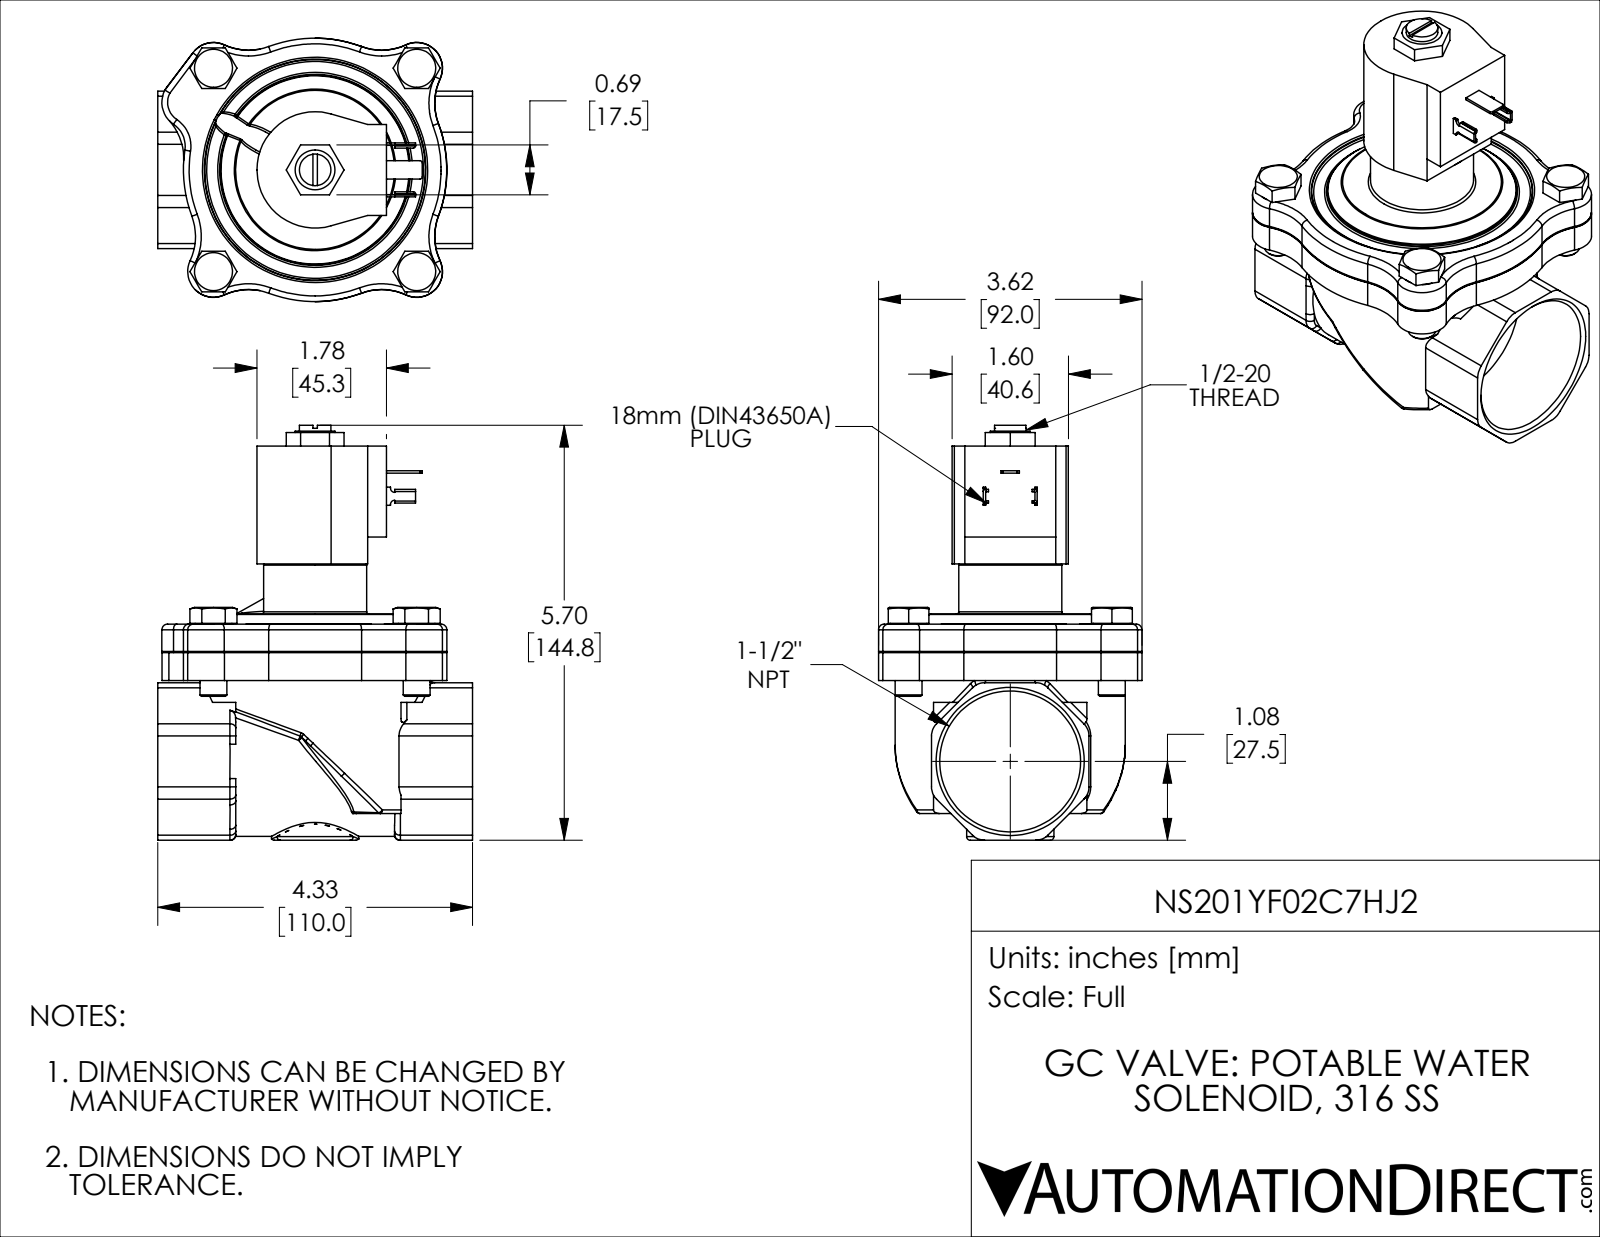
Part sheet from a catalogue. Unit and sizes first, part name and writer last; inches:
Units: inches
Overall size (bounding box): 5.701 × 4.33 × 3.622
Round holes (diameter × count): ⌀0.375 ×4, ⌀0.433 ×4, ⌀0.125 ×1, ⌀0.488 ×1, ⌀0.846 ×1, ⌀0.949 ×1, ⌀1.937 ×1
Round bosses / shafts (diameter × count): ⌀0.504 ×4, ⌀0.37 ×4, ⌀3.165 ×1, ⌀1.417 ×1, ⌀1.2 ×1, ⌀0.547 ×1, ⌀0.434 ×1
Partial cylindrical surfaces — rounded edges, fillets, slot ends (radius × count): R0.787 ×15, R0.08 ×13, R0.03 ×8, R0.236 ×8, R0.354 ×8, R0.362 ×2, R1.811 ×2, R0.031 ×1
Main face-to-face distances: 0.382, 0.775, 0.393, 3.222, 2.84, 2.447, 1.83, 1.602, 1.22, 0.827
Hole centre spacings: 2.795, 1.976, 1.977, 2.794, 2.795, 3.952, 3.953
Volume: 26.21 in³ · Surface area: 138.4 in²
Bodies: 12 solids, 541 faces (170 planar, 156 cylindrical, 215 other)
Part name (STEP PRODUCT): NS201YF02C7HJ2
STEP written by: SolidWorks 2018 (AUTOMOTIVE_DESIGN)
